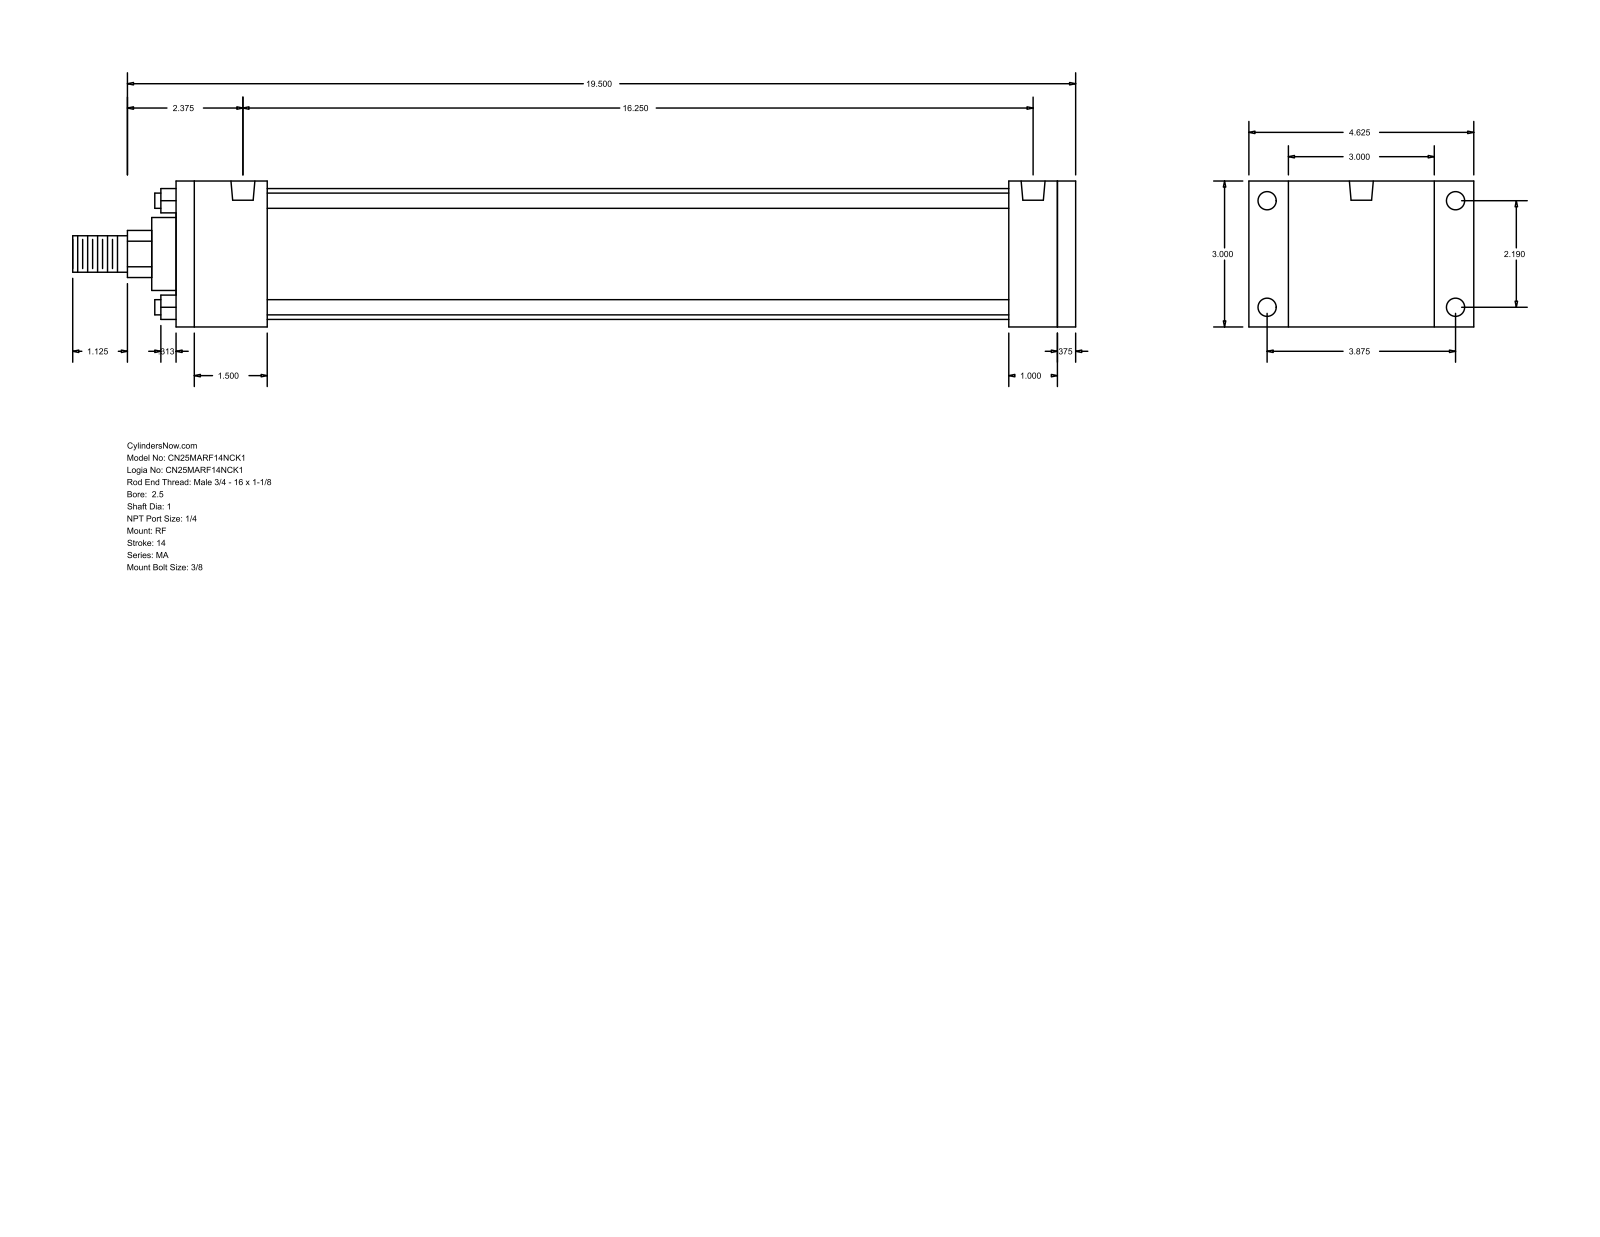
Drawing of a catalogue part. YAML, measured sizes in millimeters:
part_name: "MA_RF__0250_1"
step_written_by: "GSSL Pune (CONFIG_CONTROL_DESIGN)"
units: millimeters
bodies: {solids: 0, faces: 92, planar: 64, cylindrical: 28, other: 0}
overall_size: [523.88, 117.47, 76.2]
round_holes:
  - {diameter: 7.94, count: 4}
  - {diameter: 9.53, count: 4}
  - {diameter: 12.49, count: 2}
round_bosses_or_shafts:
  - {diameter: 7.94, count: 4}
  - {diameter: 68.33, count: 1}
  - {diameter: 38.1, count: 1}
  - {diameter: 25.4, count: 1}
  - {diameter: 19.05, count: 1}
partial_cylinders:
  - {radius: 12.29, count: 1}
face_to_face_distances: [76.2, 469.9, 9.53, 460.37, 47.63, 434.98, 387.35, 412.74, 422.27, 25.39]
hole_center_spacings: [55.62, 98.42, 113.05, 412.74]
